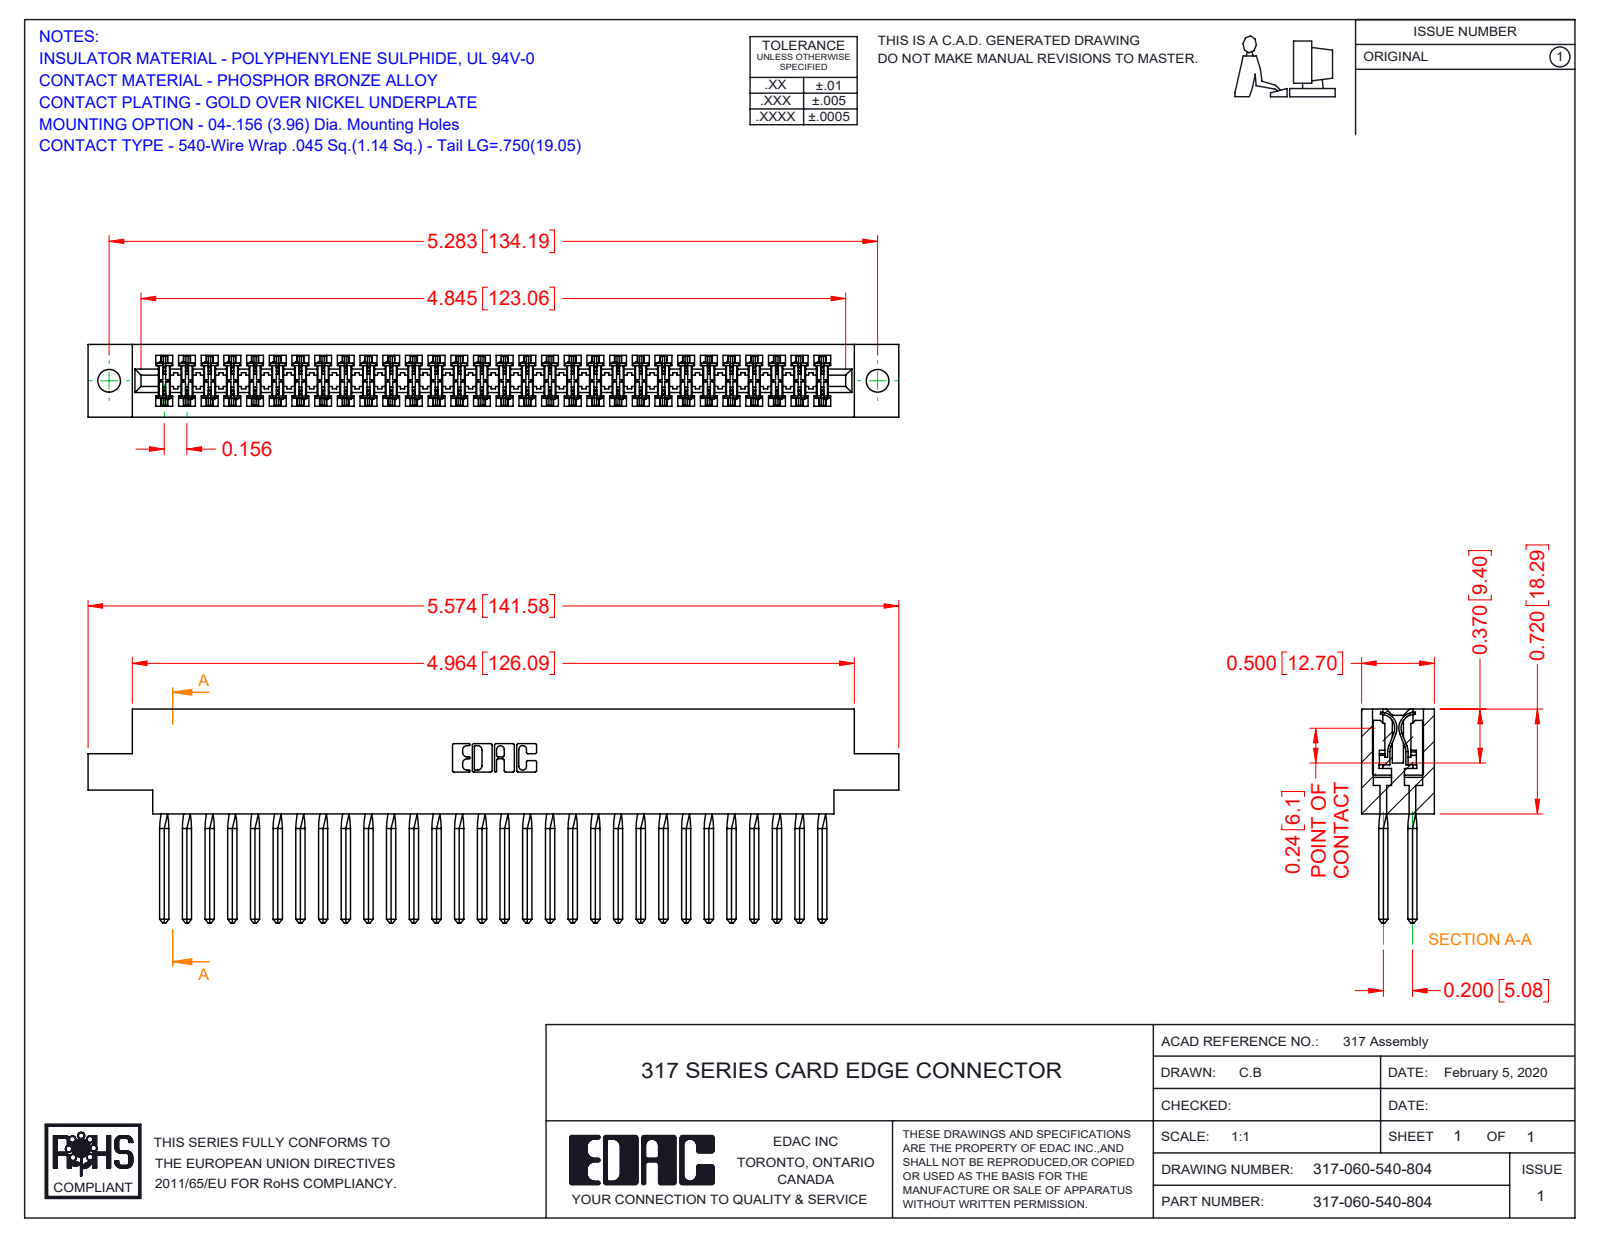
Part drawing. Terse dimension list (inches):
name: 317-290-001_540; 317 Part_.156 Dia - TH; 317-060-540-804
written by: SolidWorks 2016 (CONFIG_CONTROL_DESIGN)
unit: in
bodies: 61 solids, 5442 faces (4438 planar, 764 cylindrical, 240 other)
size: 5.574 × 1.47 × 0.5
volume: 1.42 in³; area: 52.8 in²
holes: 2× ⌀0.156
rounds: 120× R0.015, 22× R0.01, 6× R0.007, 6× R0.031, 3× R0.026, 2× R0.095, 2× R0.1, 2× R0.11
face distances: 0.5, 0.075, 0.425, 0.35, 0.11, 0.195, 0.094, 0.2, 0.72, 0.115
hole spacings: 5.283
